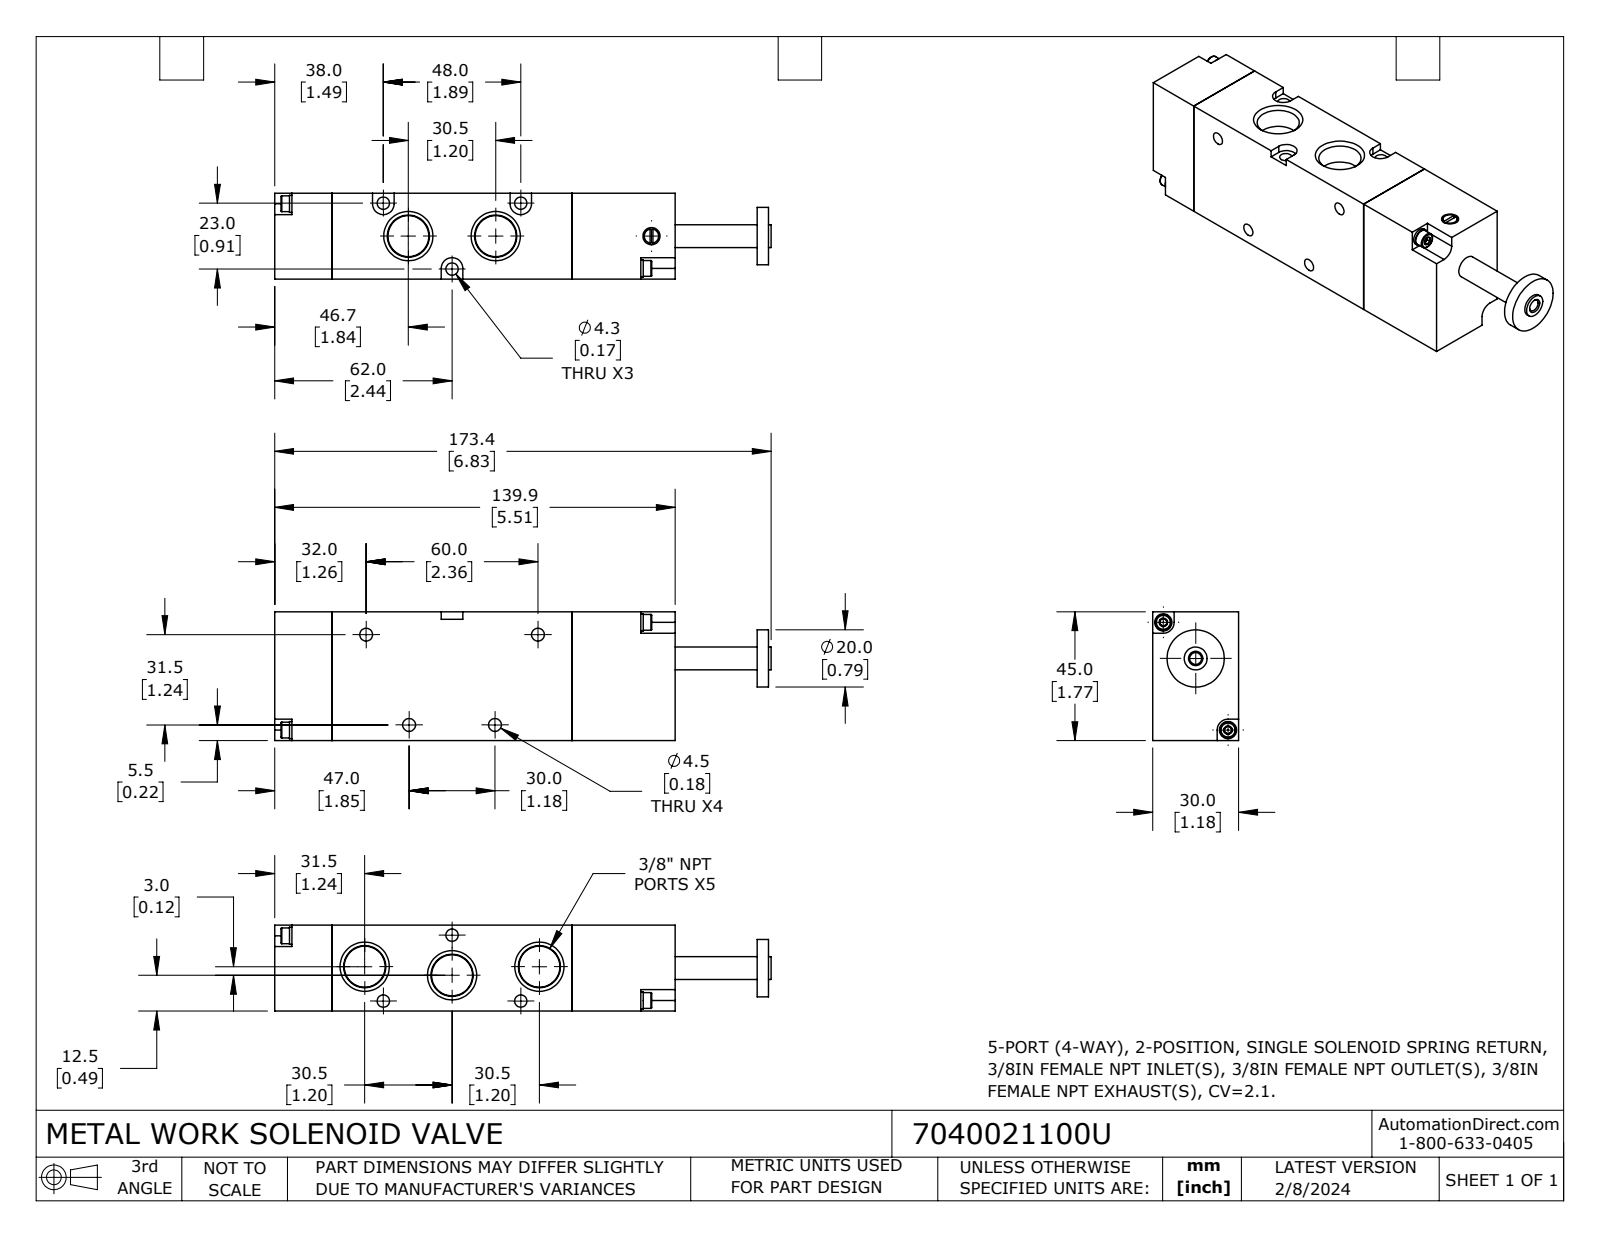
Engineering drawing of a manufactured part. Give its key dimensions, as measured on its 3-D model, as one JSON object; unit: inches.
{"part_name": "7040021100U", "step_written_by": "SolidWorks 2023 (CONFIG_CONTROL_DESIGN)", "units": "inches", "bodies": {"solids": 11, "faces": 266, "planar": 121, "cylindrical": 67, "other": 78}, "overall_size": [6.827, 1.772, 1.181], "volume_in3": 10.95, "surface_area_in2": 56.82, "round_holes": [[0.118, 4], [0.177, 4], [0.169, 3], [0.163, 1], [0.236, 1]], "round_bosses_or_shafts": [[0.236, 4], [0.217, 4], [0.787, 1], [0.315, 1], [0.197, 1]], "partial_cylinders_radius": [[0.15, 4], [0.148, 3]], "face_to_face_distances": [1.181, 1.772, 3.303, 0.787, 4.091, 5.508, 4.72, 1.417, 0.303, 1.469], "hole_center_spacings": [0.666, 0.89, 1.08, 1.309, 1.374, 1.48, 1.727, 2.163]}
